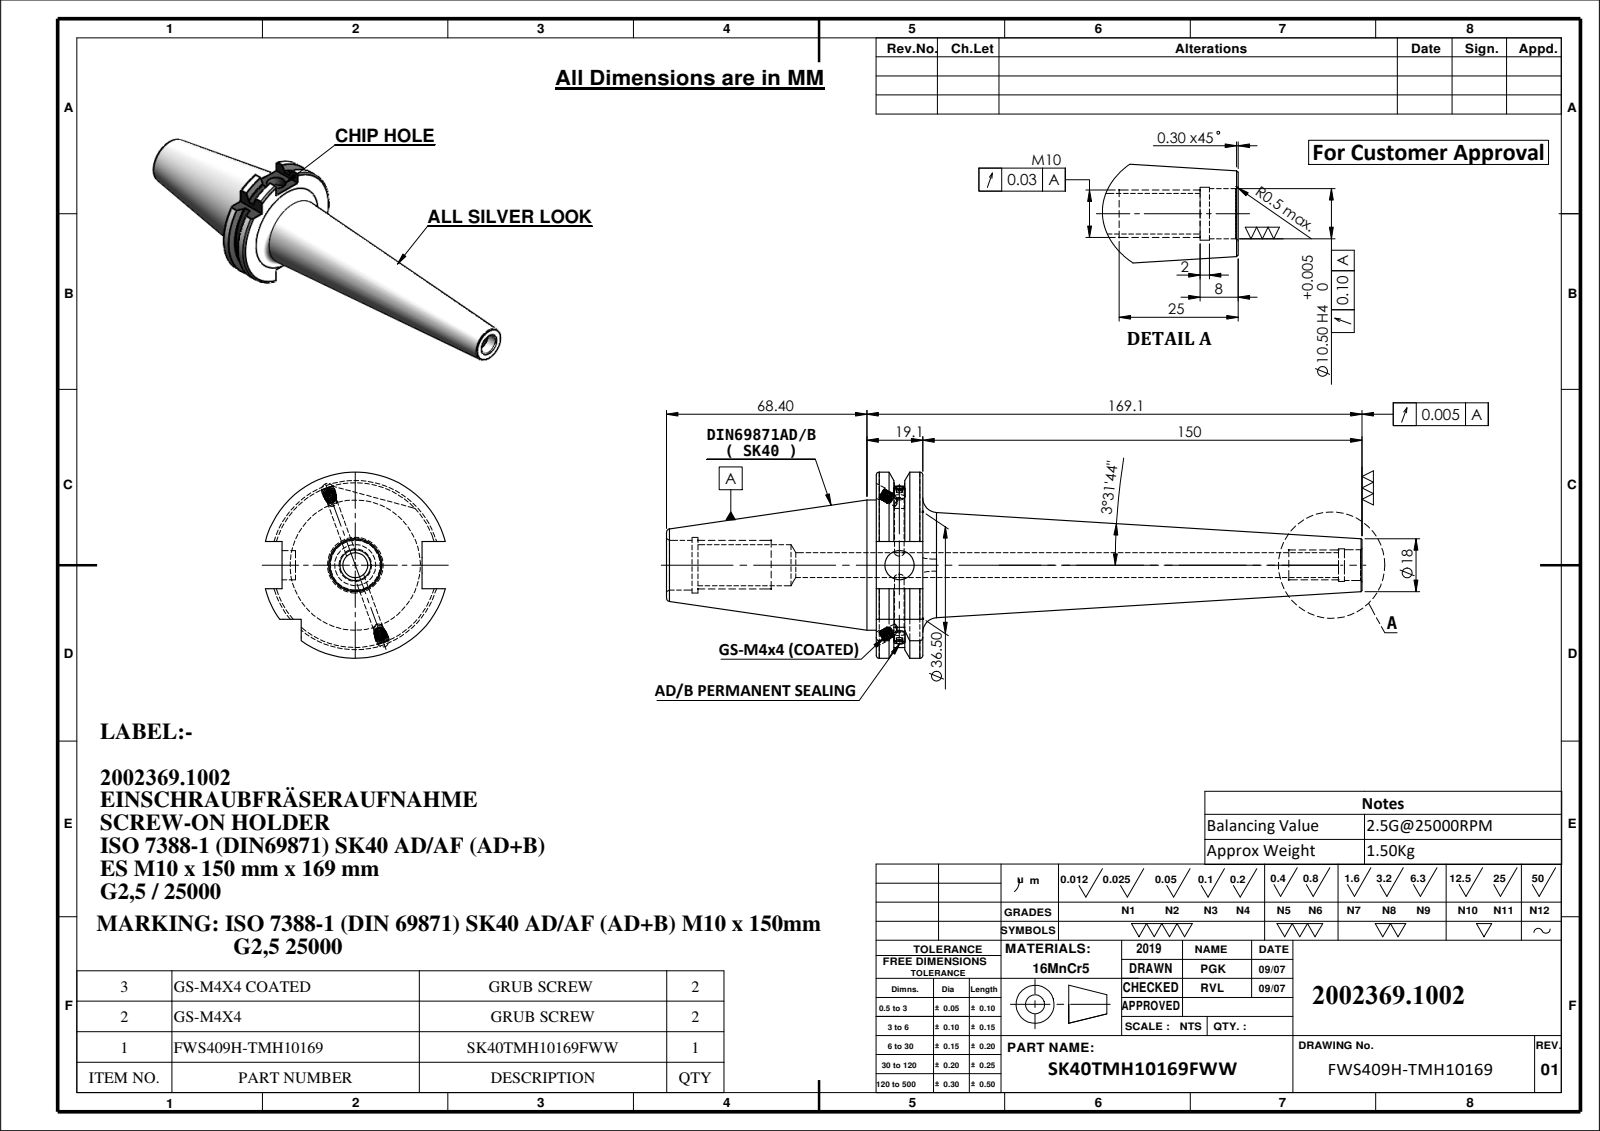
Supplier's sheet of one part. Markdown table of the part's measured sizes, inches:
| quantity | value |
| --- | --- |
| part name | M4X4_DIN 913 - M4 x 4-N; SK40TMH10169FWW; FWS409H-TMH10169; GS-M4X4-COATING_DIN 913 - M4 x 4-N |
| STEP written by | SolidWorks 2024 (CONFIG_CONTROL_DESIGN) |
| units | inches |
| bodies | 5 solids, 240 faces (64 planar, 68 cylindrical, 108 other) |
| overall size | 9.35 × 2.502 × 2.42 |
| volume | 11.31 in³ |
| surface area | 57.32 in² |
| round holes (diameter × count) | 0.13 × 3, 0.177 × 2, 0.335 × 1, 0.394 × 1, 0.413 × 1, 0.437 × 1, 0.551 × 1, 0.669 × 1, 0.748 × 1 |
| round bosses / shafts (diameter × count) | 0.157 × 4, 0.114 × 2, 1.75 × 1 |
| partial cylindrical surfaces (radius × count) | 1.107 × 1, 1.251 × 1 |
| main face-to-face distances | 0.626, 0.634, 1.882, 2.819, 3.445, 9.35, 6.531, 5.906, 0.421, 2.398 |
